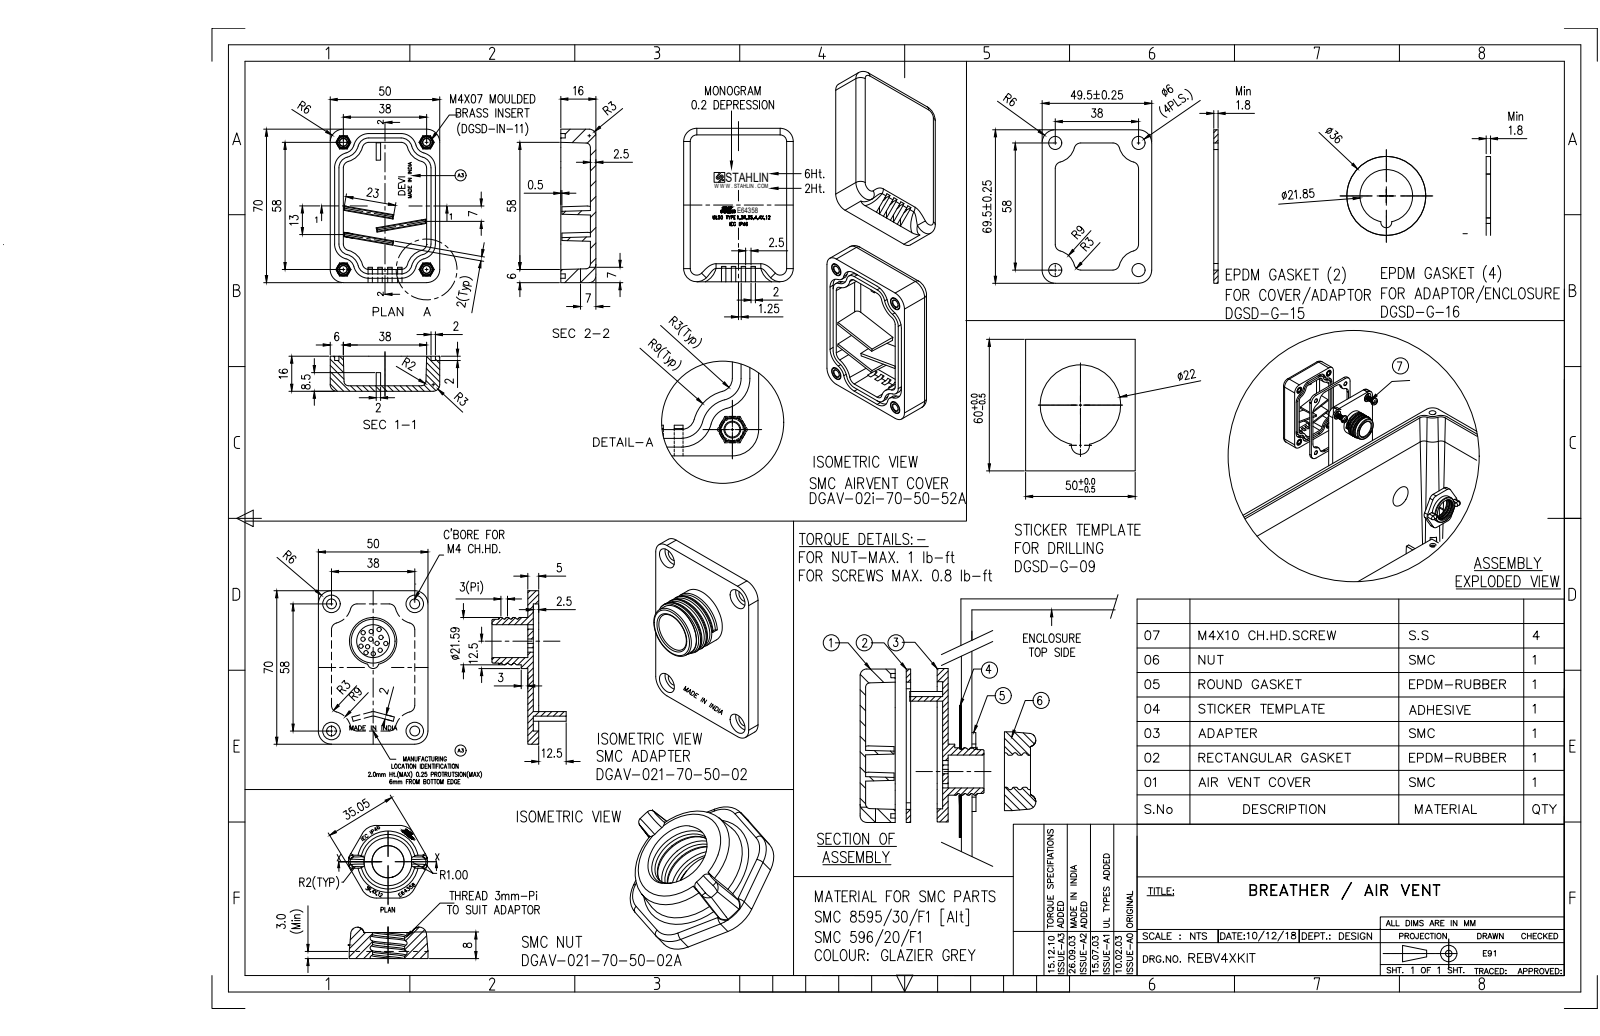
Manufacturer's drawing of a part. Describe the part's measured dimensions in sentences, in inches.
The part is named "REBV4XKIT". Its 3-D file was written by "SolidWorks 2017 (AUTOMOTIVE_DESIGN)". It is 13 solids with 2280 faces: 1784 planar, 188 cylindrical and 308 other. Overall it measures 2.756 by 1.969 by 1.608 inches. Its volume is 3.145 cubic inches and its surface area 56.83 square inches. Round holes: 11 of diameter 0.079, 4 of diameter 0.1, 4 of diameter 0.13, 4 of diameter 0.177, 4 of diameter 0.197, 1 of diameter 0.01, 1 of diameter 0.591, 1 of diameter 0.812, 1 of diameter 0.86. Round bosses or shafts: 4 of diameter 0.295, 4 of diameter 0.236, 4 of diameter 0.157, 1 of diameter 1.467, 1 of diameter 0.85, 1 of diameter 0.787. Partial cylindrical surfaces (rounded edges, fillets, slot ends): 20 of radius 0.02, 16 of radius 0.02, 8 of radius 0.197, 8 of radius 0.275, 7 of radius 0.004, 7 of radius 0.008, 7 of radius 0.039, 6 of radius 0.071. The main face-to-face distances are 0.079, 0.922, 0.709, 0.213, 0.292, 0.63, 0.125, 0.204, 0.088, 0.834. The hole center spacings are 1.004, 0.21, 0.366, 0.993, 1.496, 1.779, 2.283, 2.73.
